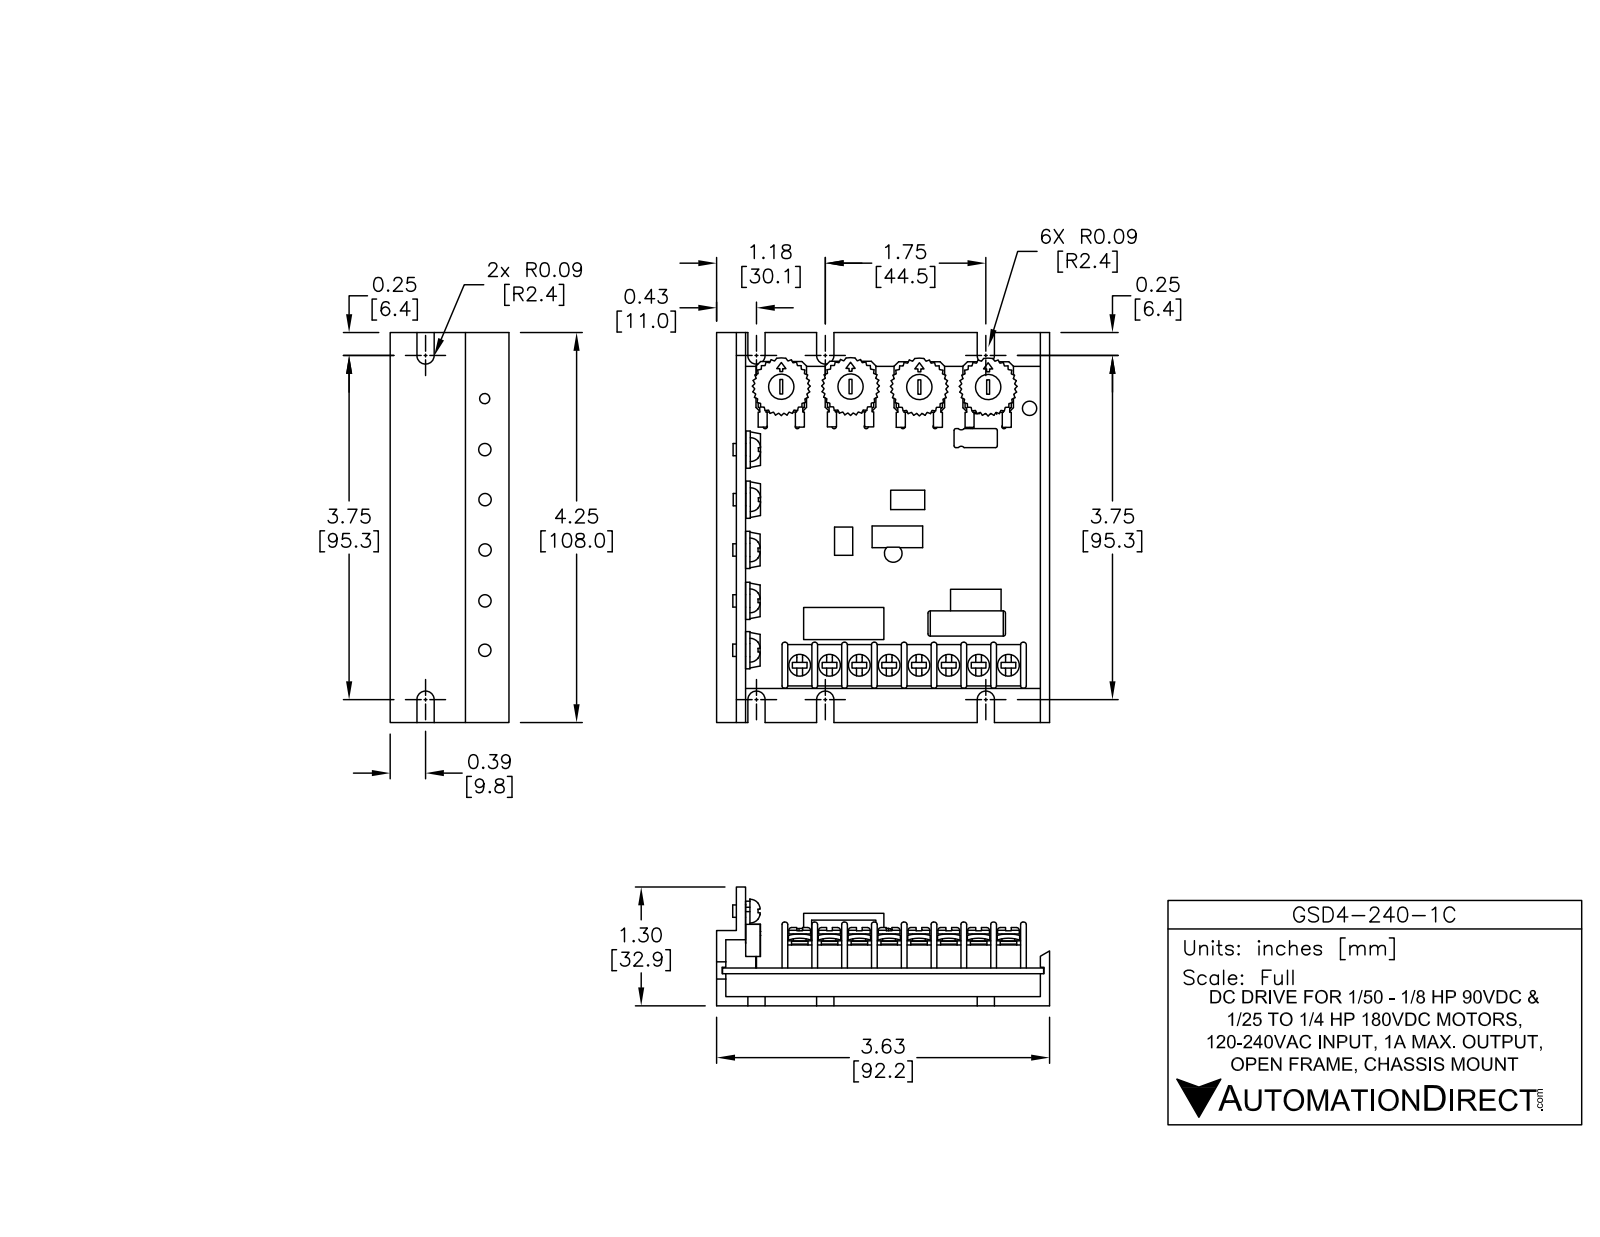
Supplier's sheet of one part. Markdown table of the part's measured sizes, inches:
| quantity | value |
| --- | --- |
| part name | Q6; GSD4-240-1C; 125_Metal; R1 (+8 more) |
| STEP written by | SolidWorks 2014 (AUTOMOTIVE_DESIGN) |
| units | inches |
| bodies | 66 solids, 4540 faces (2222 planar, 1613 cylindrical, 705 other) |
| overall size | 4.25 × 3.628 × 1.295 |
| volume | 4.359 in³ |
| surface area | 114.2 in² |
| round holes (diameter × count) | 0.033 × 90, 0.043 × 19, 0.046 × 12, 0.07 × 9, 0.035 × 8, 0.04 × 6, 0.11 × 6, 0.144 × 5, 0.111 × 4, 0.276 × 4, 0.038 × 3, 0.039 × 2 |
| round bosses / shafts (diameter × count) | 0.025 × 43, 0.024 × 30, 0.025 × 22, 0.107 × 20, 0.081 × 19, 0.08 × 19, 0.019 × 12, 0.237 × 8 |
| partial cylindrical surfaces (radius × count) | 0.025 × 56, 0.005 × 20, 0.024 × 10, 0.094 × 8, 0.39 × 8, 0.486 × 8, 0.04 × 5, 0.315 × 4 |
| main face-to-face distances | 0.1, 0.412, 0.312, 0.35, 0.25, 0.062, 0.215, 3.313, 3.528, 0.315 |
| hole center spacings | 0.55, 0.1, 0.461, 0.751, 0.2, 0.636, 1.1, 0.3 |
